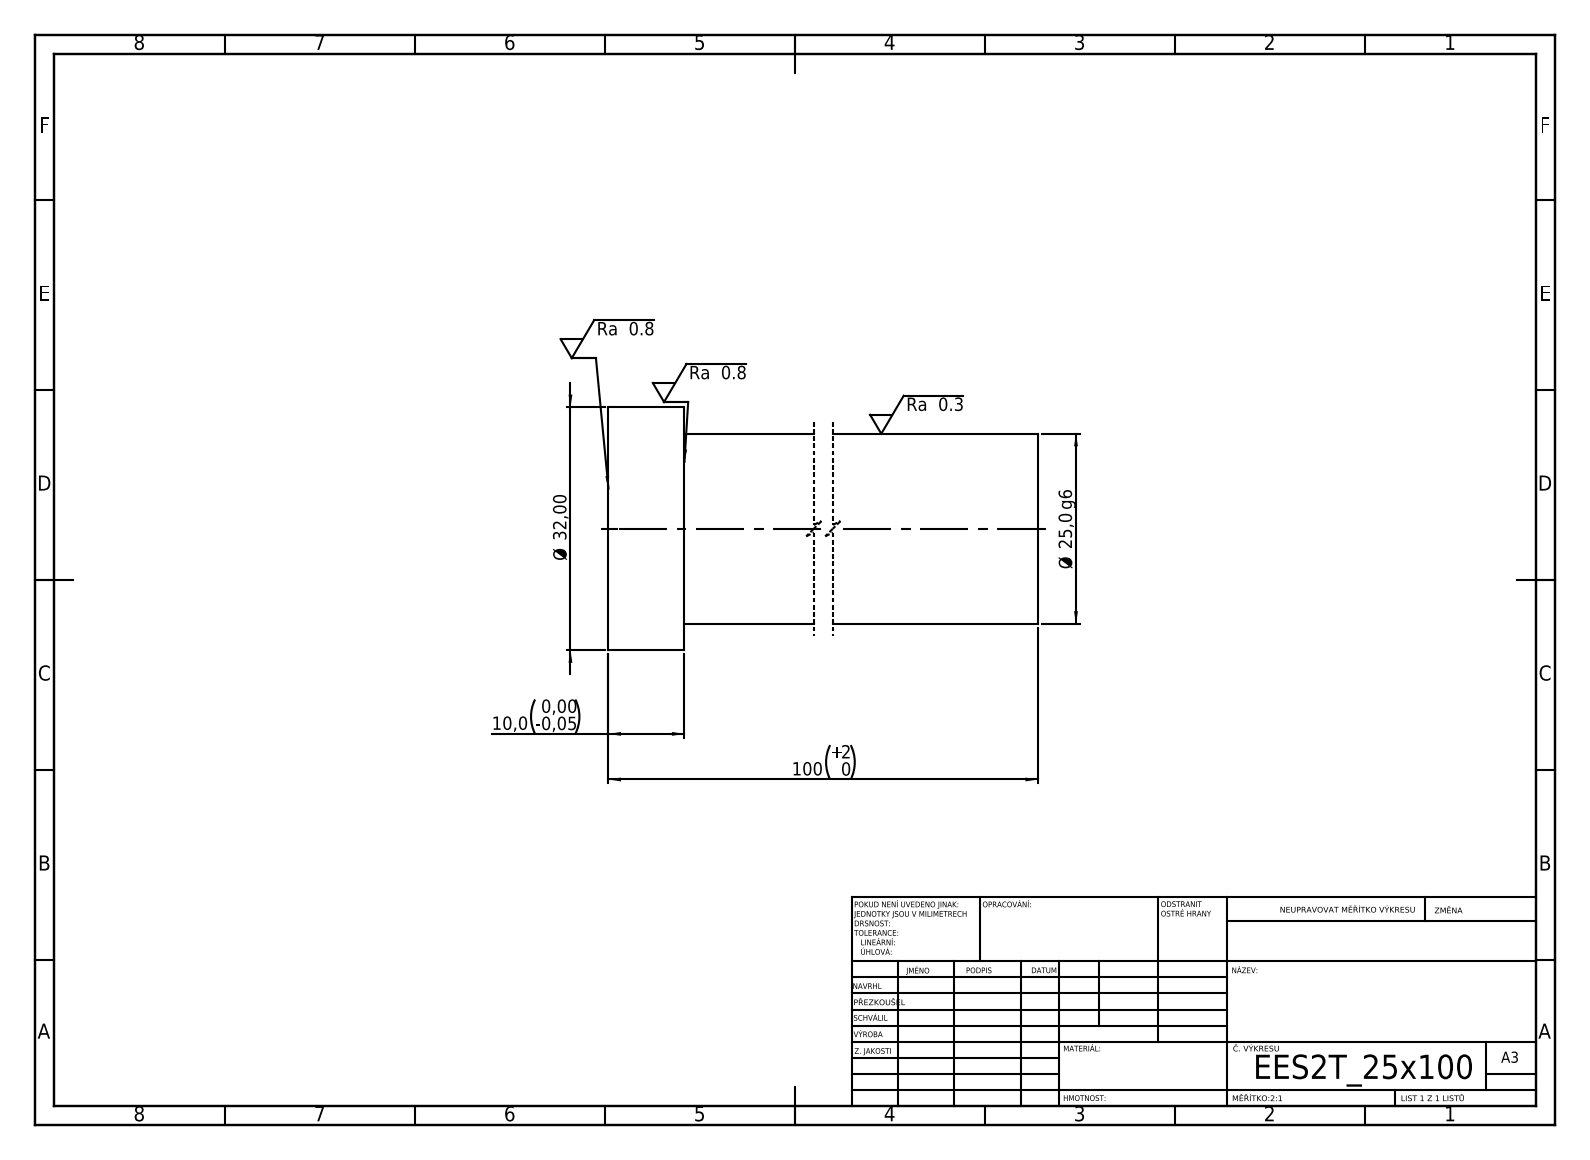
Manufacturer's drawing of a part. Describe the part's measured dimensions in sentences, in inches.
Its 3-D file was written by "SolidWorks 2019 (CONFIG_CONTROL_DESIGN)". It is 1 solid with 7 faces: 3 planar, 4 cylindrical and 0 other. Overall it measures 3.937 by 1.26 by 1.26 inches. Its volume is 3.187 cubic inches and its surface area 15.01 square inches. Round bosses or shafts: 1 of diameter 1.26, 1 of diameter 0.984. The main face-to-face distances are 3.937, 0.394, 3.543.
